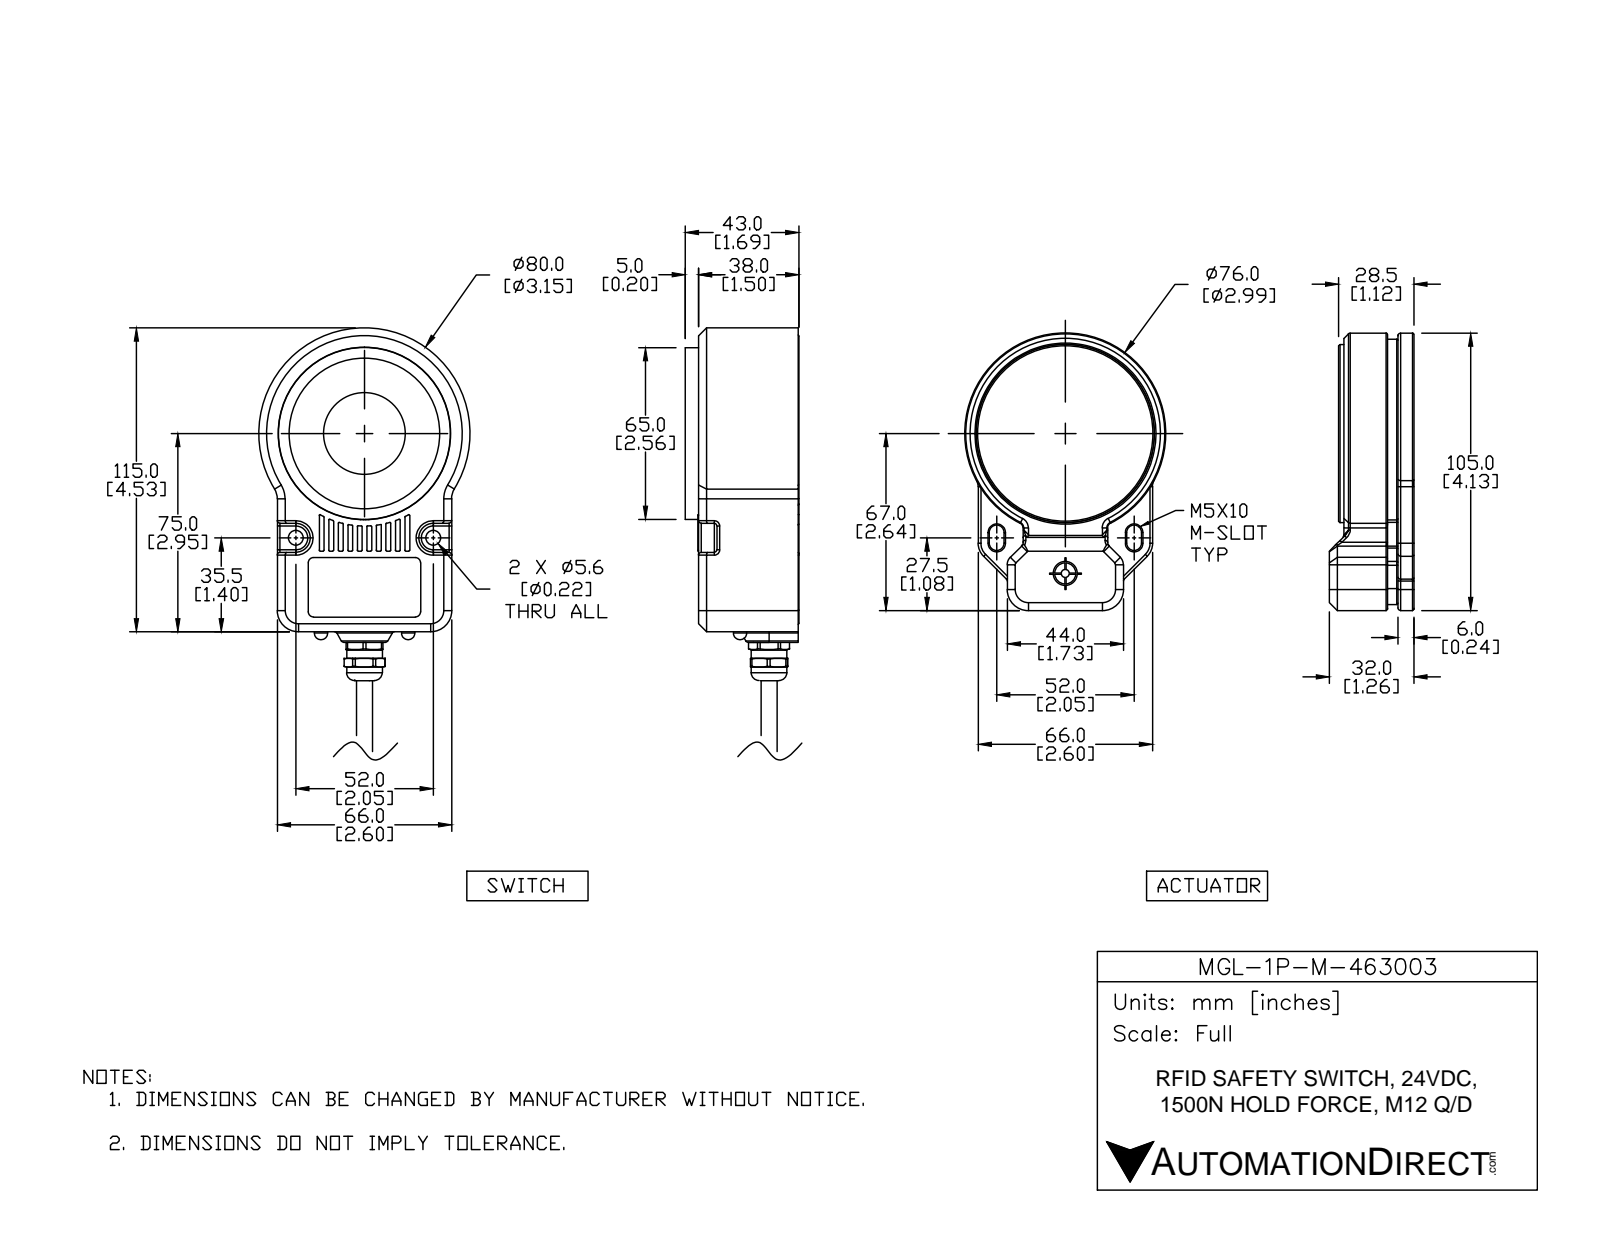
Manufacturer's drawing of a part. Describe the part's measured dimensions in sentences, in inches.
The part is named "MGL-1P-U-463003; MGL-1P-U-463003_1; MGL-1P-U-463003_2". Its 3-D file was written by "SolidWorks 2017 (AUTOMOTIVE_DESIGN)". It is 17 solids with 1674 faces: 449 planar, 708 cylindrical and 517 other. Overall it measures 8.163 by 3.15 by 2.854 inches. Its volume is 18.96 cubic inches and its surface area 210.2 square inches. Round holes: 6 of diameter 0.197, 5 of diameter 0.453, 4 of diameter 0.094, 3 of diameter 0.315, 2 of diameter 0.079, 2 of diameter 0.13, 2 of diameter 0.22, 2 of diameter 0.276, 2 of diameter 0.354, 1 of diameter 0.157, 1 of diameter 0.252, 1 of diameter 0.266. Round bosses or shafts: 4 of diameter 0.02, 3 of diameter 0.472, 3 of diameter 0.079, 2 of diameter 0.228, 2 of diameter 0.213, 2 of diameter 0.154, 2 of diameter 0.047, 1 of diameter 2.992. Partial cylindrical surfaces (rounded edges, fillets, slot ends): 187 of radius 0.02, 75 of radius 0.039, 39 of radius 0.012, 18 of radius 0.079, 7 of radius 0.024, 7 of radius 0.315, 6 of radius 0.157, 6 of radius 0.217. The main face-to-face distances are 0.236, 0.315, 0.098, 2.303, 2.618, 0.413, 2.205, 0.118, 0.65, 2.854. The hole center spacings are 0.787, 0.984, 1.392, 1.364, 0.173, 0.349, 0.4, 0.406.
